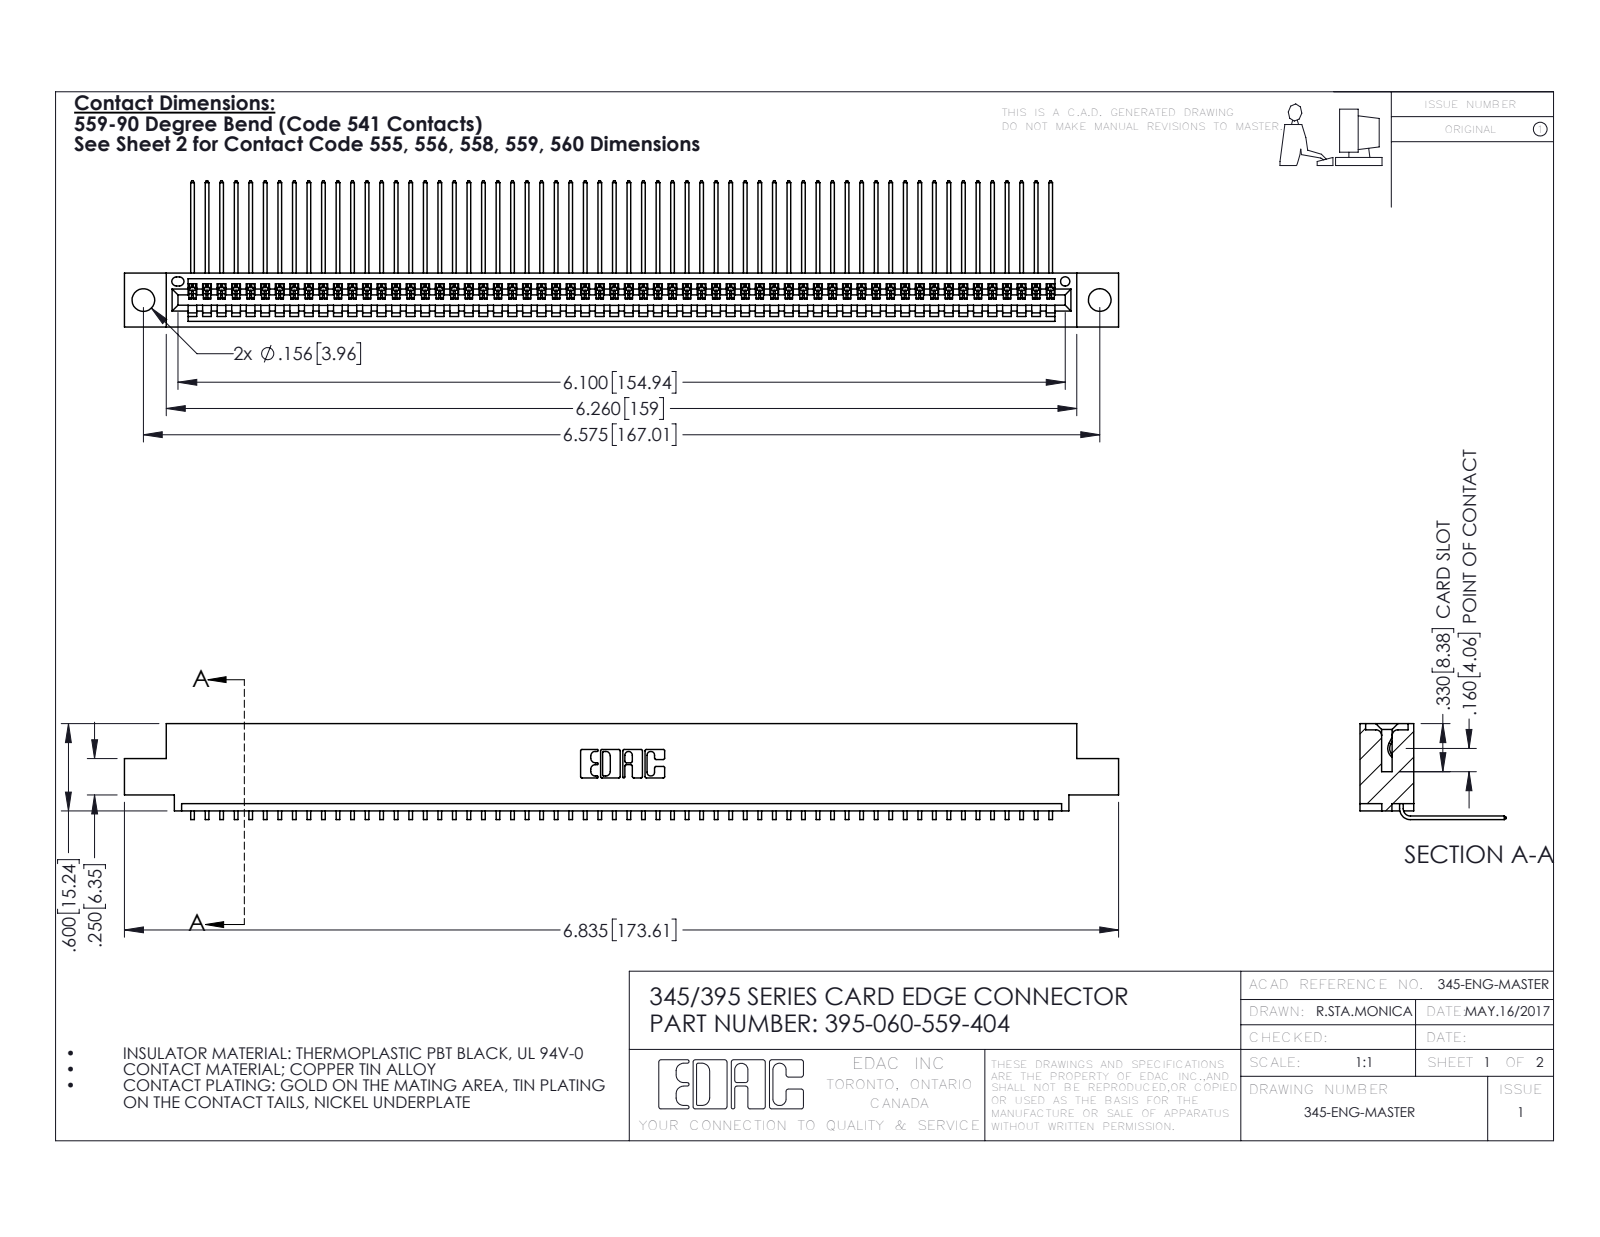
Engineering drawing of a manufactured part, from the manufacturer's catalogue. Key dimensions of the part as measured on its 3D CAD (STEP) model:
Part name (STEP PRODUCT): 345 Part_0.110 Offset - 0.156 Dia-TH; 395-060-559-404; 345-292-001_558 559 Tail - 1
STEP written by: SolidWorks 2016 (CONFIG_CONTROL_DESIGN)
Units: inches
Bodies: 61 solids, 3730 faces (2604 planar, 1126 cylindrical, 0 other)
Overall size (bounding box): 6.835 × 1.005 × 0.659
Volume: 1.018 in³ · Surface area: 36.38 in²
Round holes (diameter × count): ⌀0.156 ×2, ⌀0.064 ×1
Partial cylindrical surfaces — rounded edges, fillets, slot ends (radius × count): R0.006 ×120, R0.01 ×22, R0.007 ×6, R0.031 ×6, R0.026 ×3, R0.031 ×2, R0.04 ×2, R0.014 ×1
Main face-to-face distances: 0.072, 0.298, 0.37, 0.2, 0.098, 0.272, 0.025, 0.225, 0.149, 0.072
Hole centre spacings: 0.27, 6.339, 6.575
